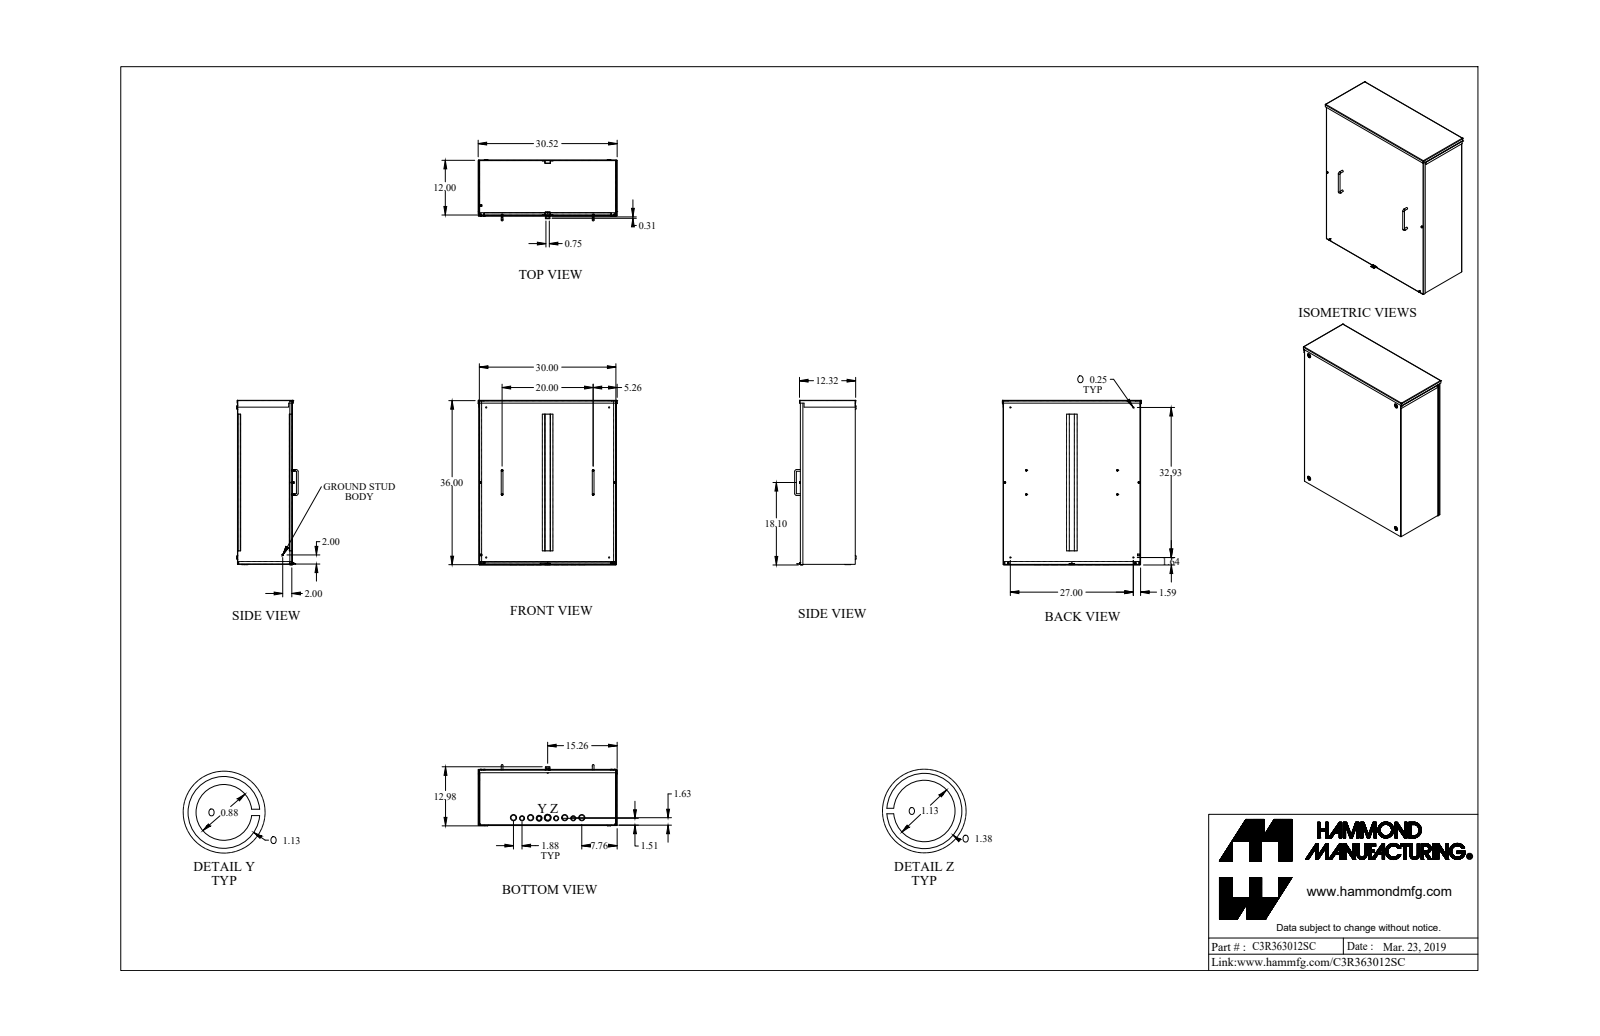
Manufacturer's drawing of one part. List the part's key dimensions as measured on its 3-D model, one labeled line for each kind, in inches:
Part name (STEP PRODUCT): C3R363012SC_Default
STEP written by: SolidWorks 2019 (CONFIG_CONTROL_DESIGN)
Units: inches
Bodies: 19 solids, 653 faces (342 planar, 193 cylindrical, 118 other)
Overall size (bounding box): 36.135 × 30.519 × 13.478
Volume: 300.5 in³ · Surface area: 8 365 in²
Round holes (diameter × count): ⌀0.156 ×5, ⌀0.17 ×4, ⌀0.203 ×4, ⌀0.25 ×4, ⌀1.125 ×3, ⌀0.875 ×2, ⌀0.875 ×2, ⌀1.125 ×2, ⌀0.125 ×1, ⌀0.137 ×1
Round bosses / shafts (diameter × count): ⌀0.375 ×9, ⌀0.19 ×8, ⌀1.125 ×4, ⌀0.367 ×4, ⌀1.375 ×3, ⌀1.375 ×2, ⌀0.375 ×2, ⌀0.125 ×1
Partial cylindrical surfaces — rounded edges, fillets, slot ends (radius × count): R0.036 ×28, R0.108 ×28, R0.109 ×8, R0.125 ×8, R0.156 ×2, R0.029 ×1, R0.086 ×1
Main face-to-face distances: 0.072, 12, 11.928, 12.072, 29.928, 0.072, 30, 29.856, 35.856, 35.928
Hole centre spacings: 20, 3.75, 0.024, 1.879, 1.88, 5.3, 5.392, 5.627
